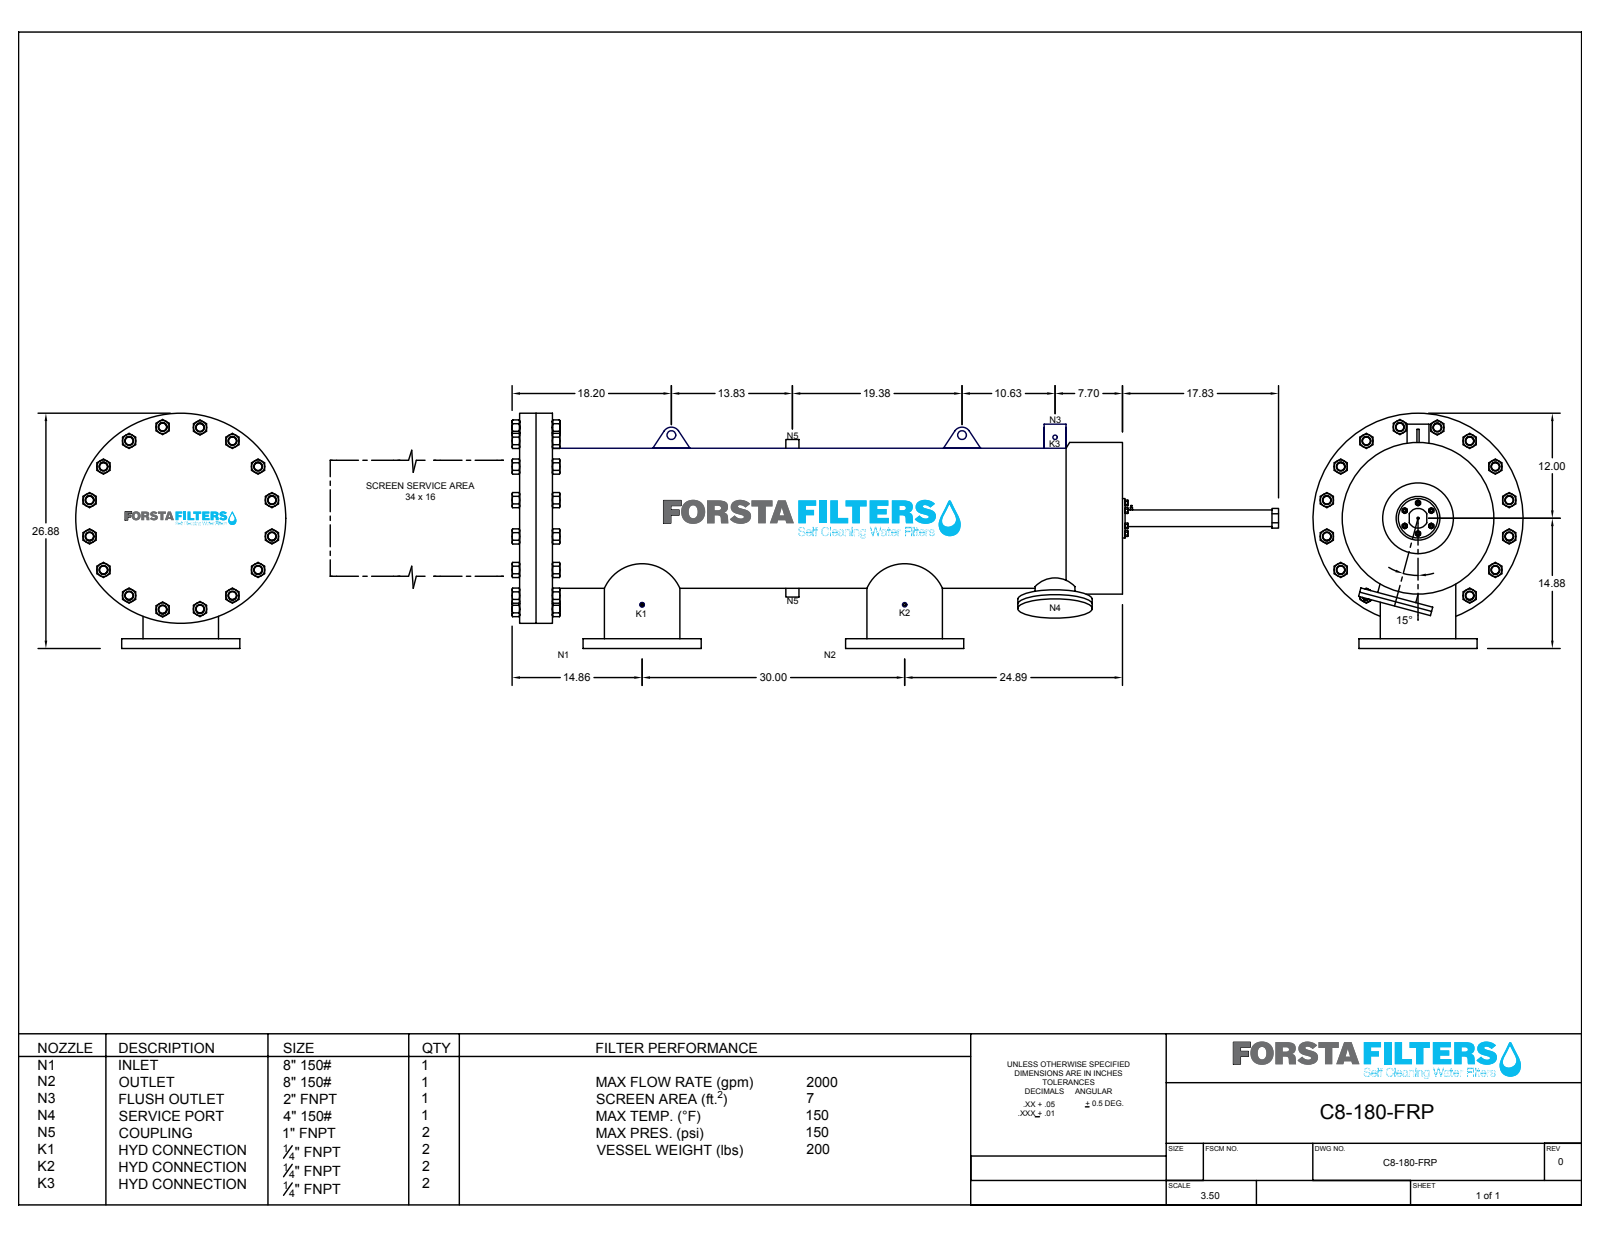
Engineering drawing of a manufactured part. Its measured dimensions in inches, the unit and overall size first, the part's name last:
Units: inches
Overall size (bounding box): 87.395 × 26.88 × 24
Round holes (diameter × count): ⌀1 ×19, ⌀0.75 ×16, ⌀0.88 ×16, ⌀0.25 ×3, ⌀4 ×2, ⌀8 ×2, ⌀0.246 ×1, ⌀1.507 ×1, ⌀2 ×1, ⌀15.603 ×1, ⌀16.934 ×1
Round bosses / shafts (diameter × count): ⌀0.375 ×6, ⌀13.5 ×2, ⌀9 ×2, ⌀8.394 ×2, ⌀4.394 ×2, ⌀0.644 ×2, ⌀24 ×1, ⌀17.328 ×1
Partial cylindrical surfaces — rounded edges, fillets, slot ends (radius × count): R1 ×2, R1.125 ×1
Main face-to-face distances: 1.875, 3.75, 1.875, 68.891, 67.017, 65.141, 68.694, 66.82, 64.944, 0.197
Hole centre spacings: 2.87, 3.75, 4.146, 5.303, 5.875, 6.929, 8.132, 8.309
Volume: 2 459 in³ · Surface area: 11 206 in²
Bodies: 22 solids, 696 faces (362 planar, 330 cylindrical, 4 other)
Part name (STEP PRODUCT): C8-FRP-180
STEP written by: SolidWorks 2018 (CONFIG_CONTROL_DESIGN)
